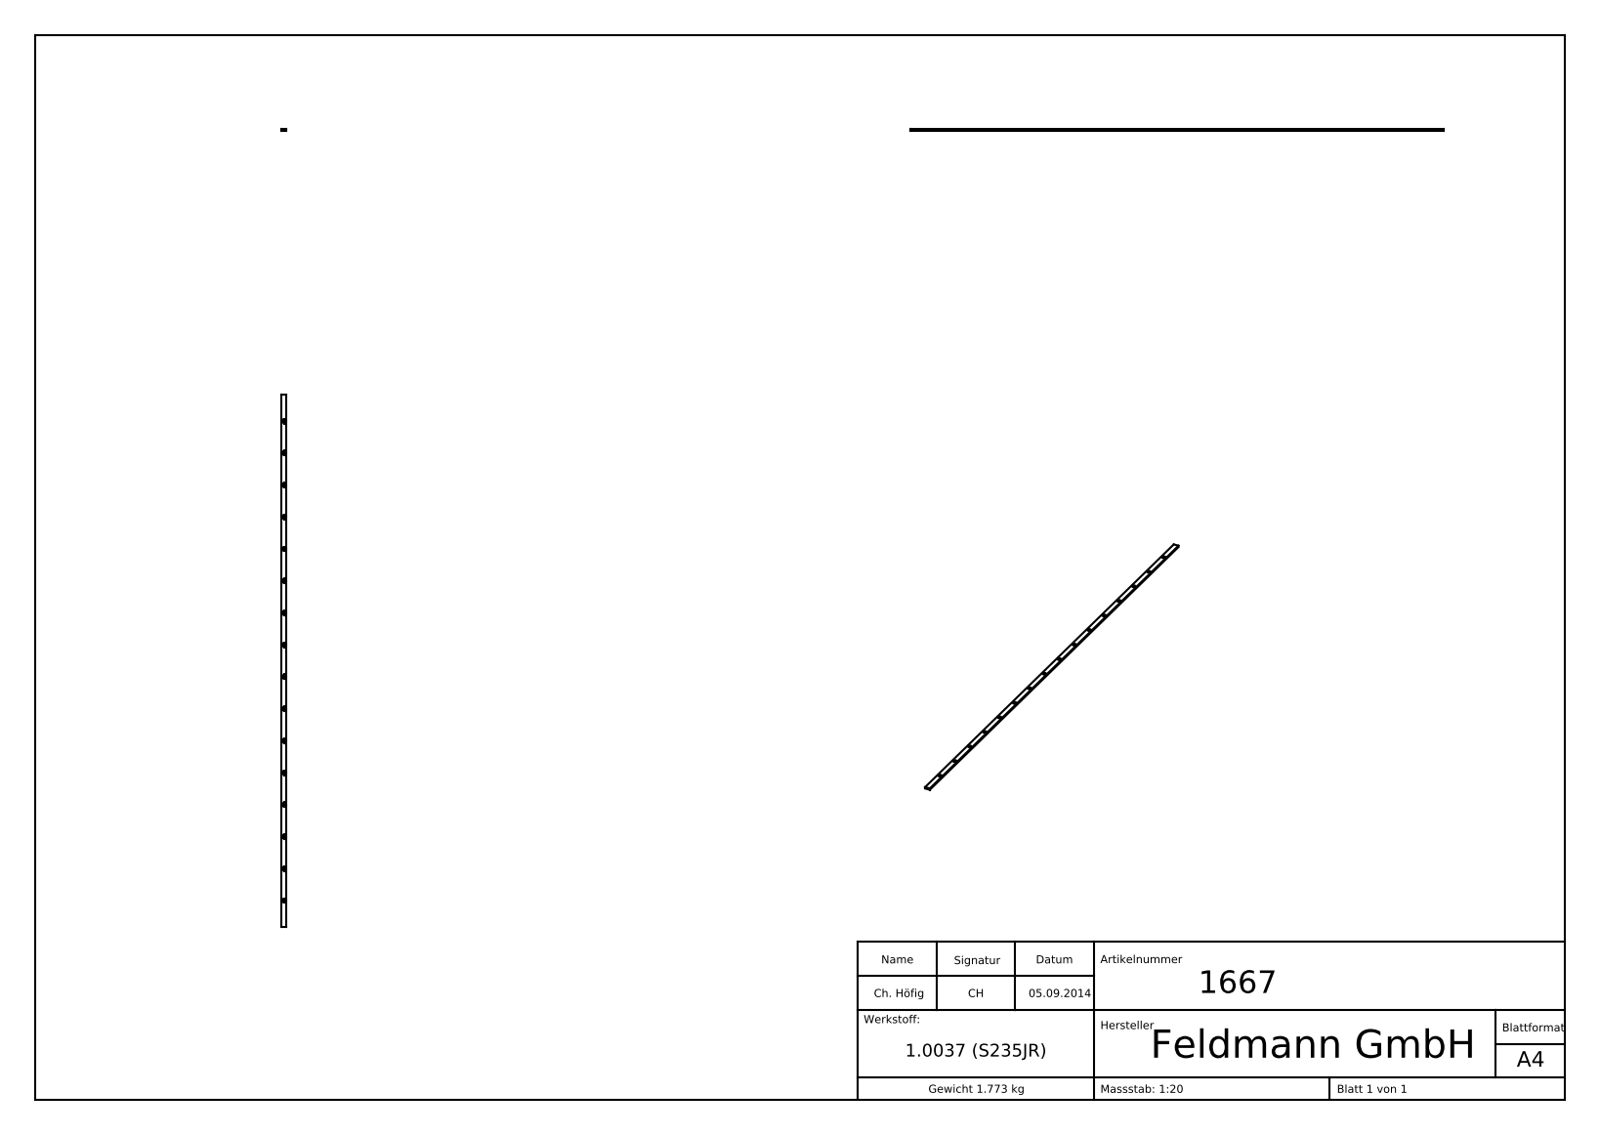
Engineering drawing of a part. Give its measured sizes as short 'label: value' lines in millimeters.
name: 1667
written by: SolidWorks 2015 (CONFIG_CONTROL_DESIGN)
unit: mm
bodies: 1 solid, 151 faces (71 planar, 32 cylindrical, 48 other)
size: 2000 × 20 × 6
volume: 227 256 mm³; area: 103 937 mm²
holes: 16× ⌀13
face distances: 6, 20, 2000, 1999.5, 0.5, 0.39, 2.97, 1.12, 1.9, 4.09
hole spacings: 120, 240, 360, 480, 600, 720, 840, 960
